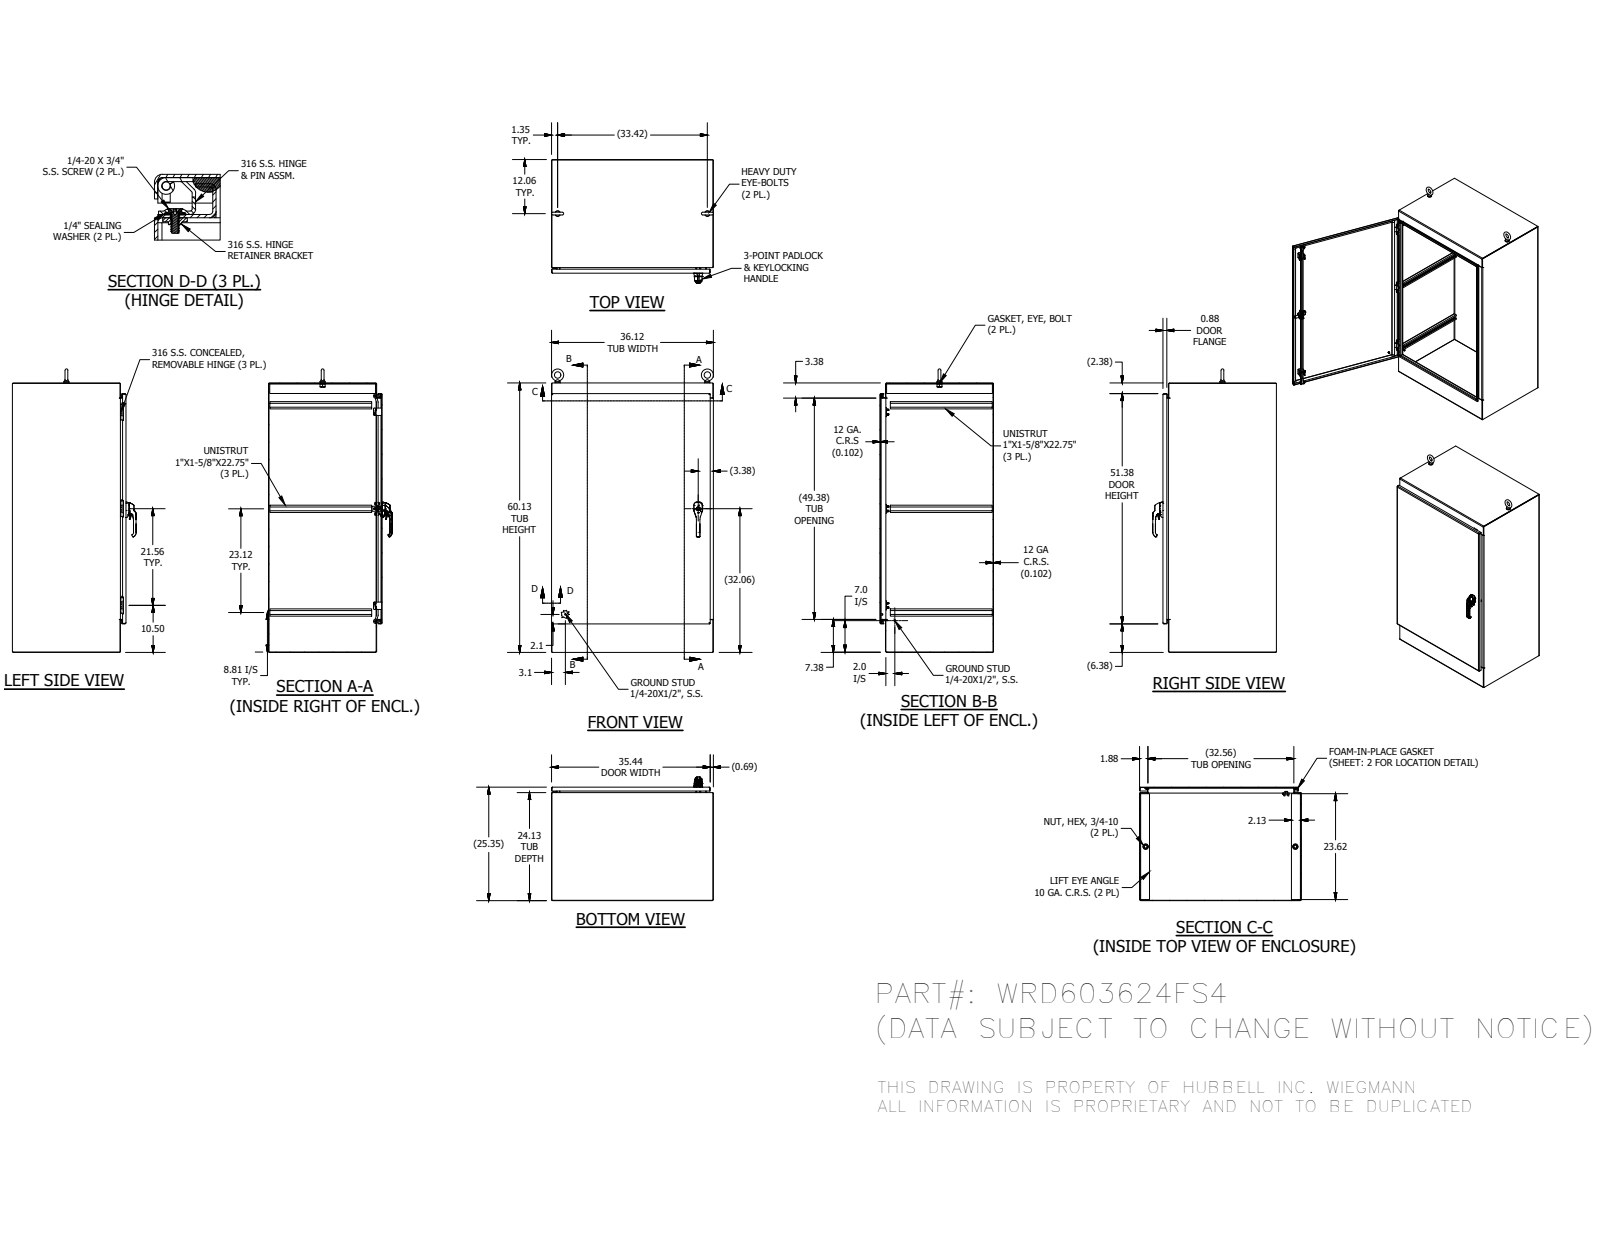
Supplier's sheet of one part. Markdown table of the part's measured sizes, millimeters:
| quantity | value |
| --- | --- |
| part name | WRD603624FS4BLR; WRD3624FS4TOP; WRD3624FS4BTM; WRD6036FS4DR (+8 more) |
| STEP written by | Autodesk Inventor 2016 (AUTOMOTIVE_DESIGN) |
| units | millimeters |
| bodies | 76 solids, 3319 faces (1322 planar, 1133 cylindrical, 864 other) |
| overall size | 1606.49 × 917.63 × 701.44 |
| volume | 18 480 000 mm³ |
| surface area | 13 920 000 mm² |
| round holes (diameter × count) | 7.02 × 8, 5.84 × 6, 7.14 × 6, 16.51 × 6, 5.08 × 4, 5.4 × 3, 6 × 3, 7.11 × 3, 6.13 × 2, 6.35 × 2, 6.41 × 2, 10.16 × 2 |
| round bosses / shafts (diameter × count) | 6.35 × 12, 15.88 × 6, 10.25 × 6, 4.63 × 6, 31.75 × 2, 28.45 × 2, 25.4 × 2, 19.05 × 2 |
| partial cylindrical surfaces (radius × count) | 0.5 × 164, 0.3 × 86, 0.25 × 22, 1.59 × 21, 0.47 × 19, 3.17 × 18, 2 × 15, 1.27 × 14 |
| main face-to-face distances | 2.59, 641.23, 914.99, 638.64, 643.82, 1524.59, 912.4, 917.58, 610.19, 31.04 |
| hole center spacings | 12.5, 547.69, 6.5, 22.5, 25.4, 51.5, 1090.4, 6 |
